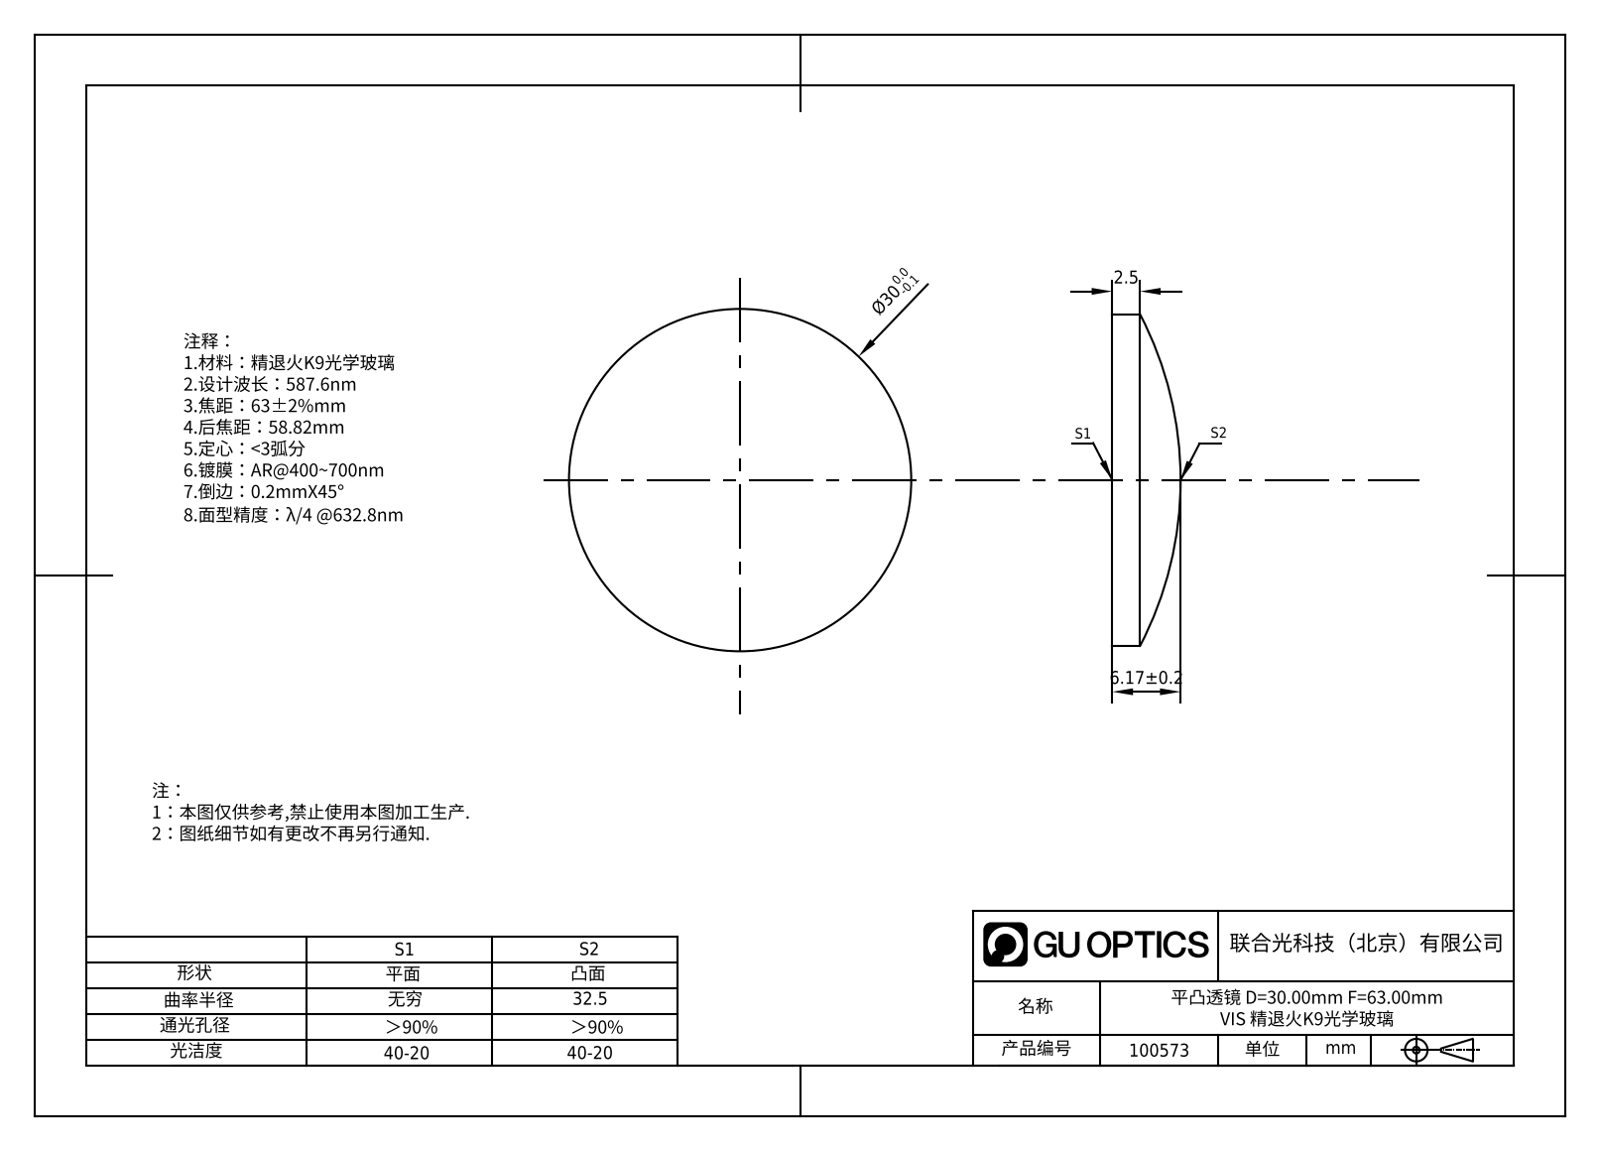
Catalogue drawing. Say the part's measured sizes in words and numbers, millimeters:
The part is named "100573". Its 3-D file was written by "SolidWorks 2020 (CONFIG_CONTROL_DESIGN)". It is 1 solid with 5 faces: 1 planar, 2 cylindrical and 2 other. Overall it measures 30 by 30 by 6.17 millimeters. Its volume is 3 090 cubic millimeters and its surface area 1 692 square millimeters. Round bosses or shafts: 1 of diameter 30.
